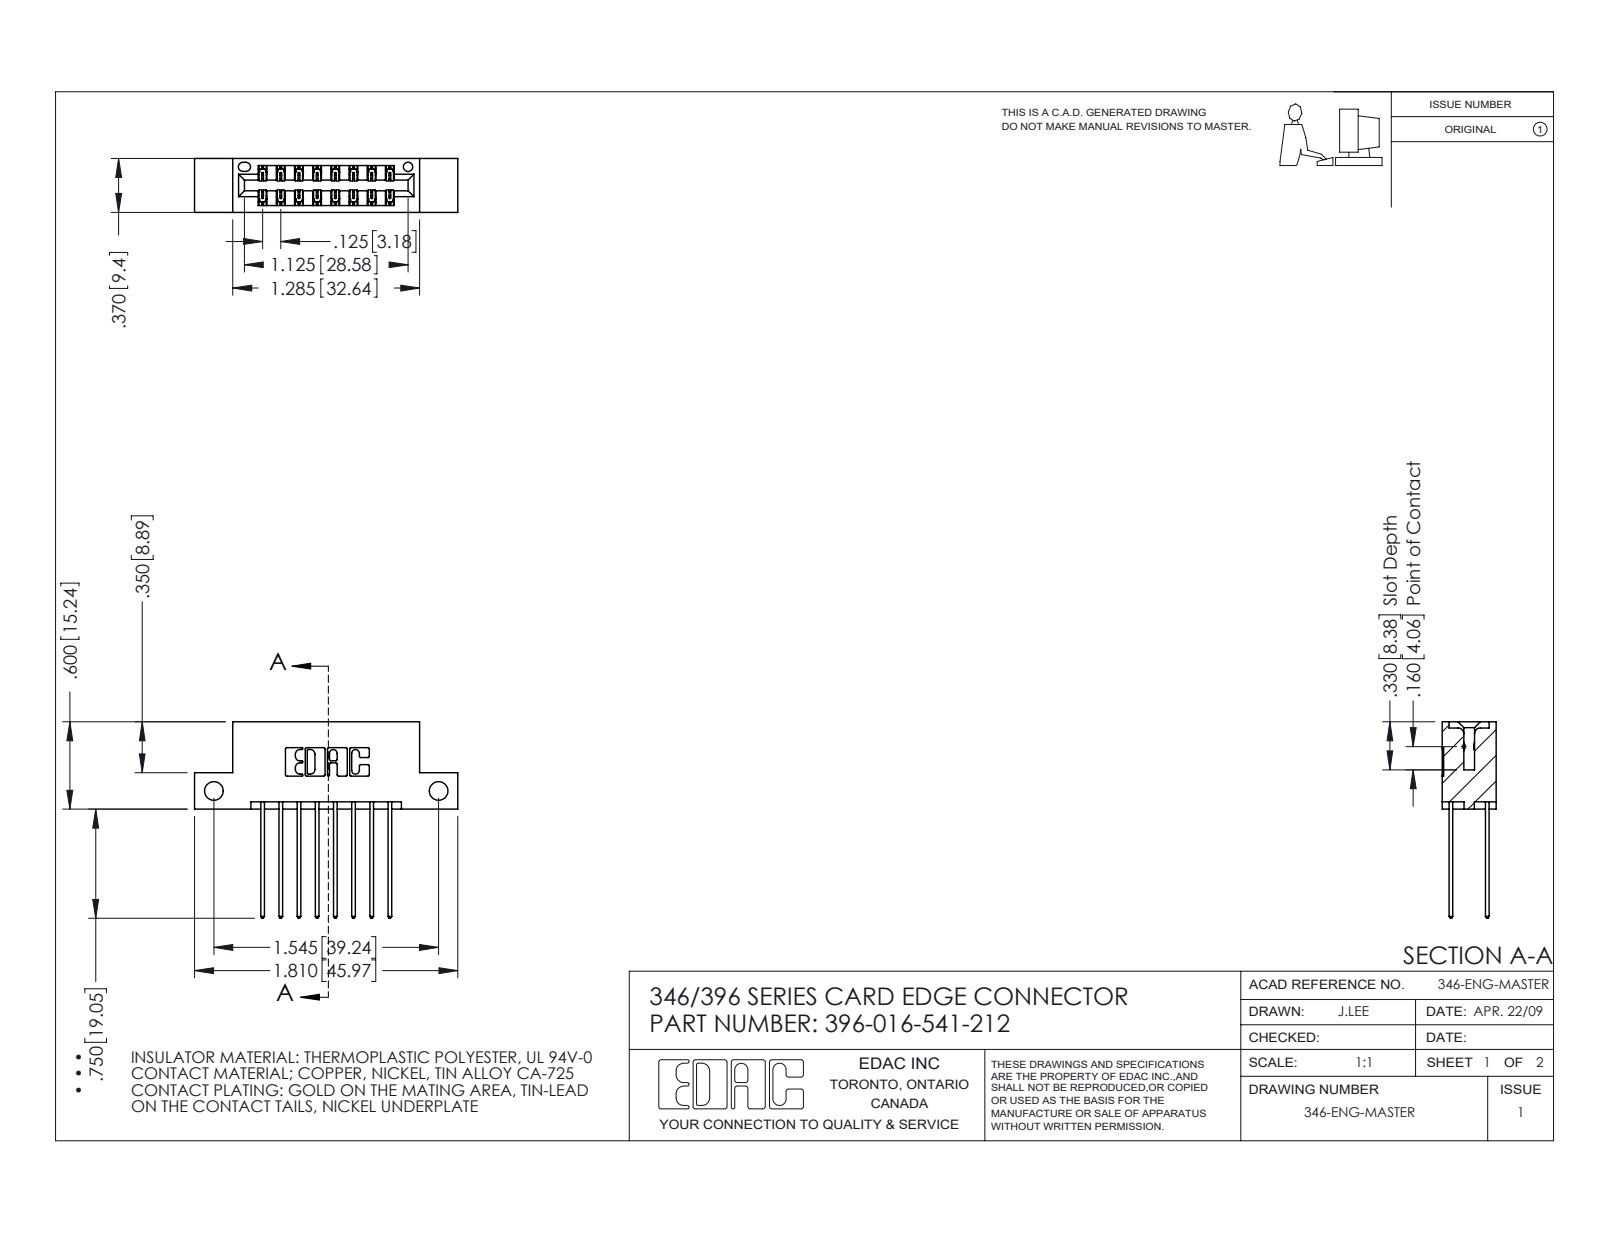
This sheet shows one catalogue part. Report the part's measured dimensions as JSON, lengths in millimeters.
{"part_name": "396-016-541-212; 346 Part_Flush Mounting Lugs - Side Mount; 345-292-001_345-293-141", "step_written_by": "SolidWorks 2016 (CONFIG_CONTROL_DESIGN)", "units": "millimeters", "bodies": {"solids": 17, "faces": 954, "planar": 636, "cylindrical": 318, "other": 0}, "overall_size": [46, 34.3, 9.4], "volume_mm3": 4230, "surface_area_mm2": 5574, "round_holes": [[3.3, 2], [1.6, 1]], "partial_cylinders_radius": [[0.2, 24], [0.3, 22], [0.3, 16], [0.2, 6], [0.8, 6], [0.7, 3], [0.4, 2], [0.6, 2]], "face_to_face_distances": [6.4, 1.2, 8.2, 9.4, 1.8, 7.6, 0.6, 7, 12.7, 3.8], "hole_center_spacings": [39.2]}
